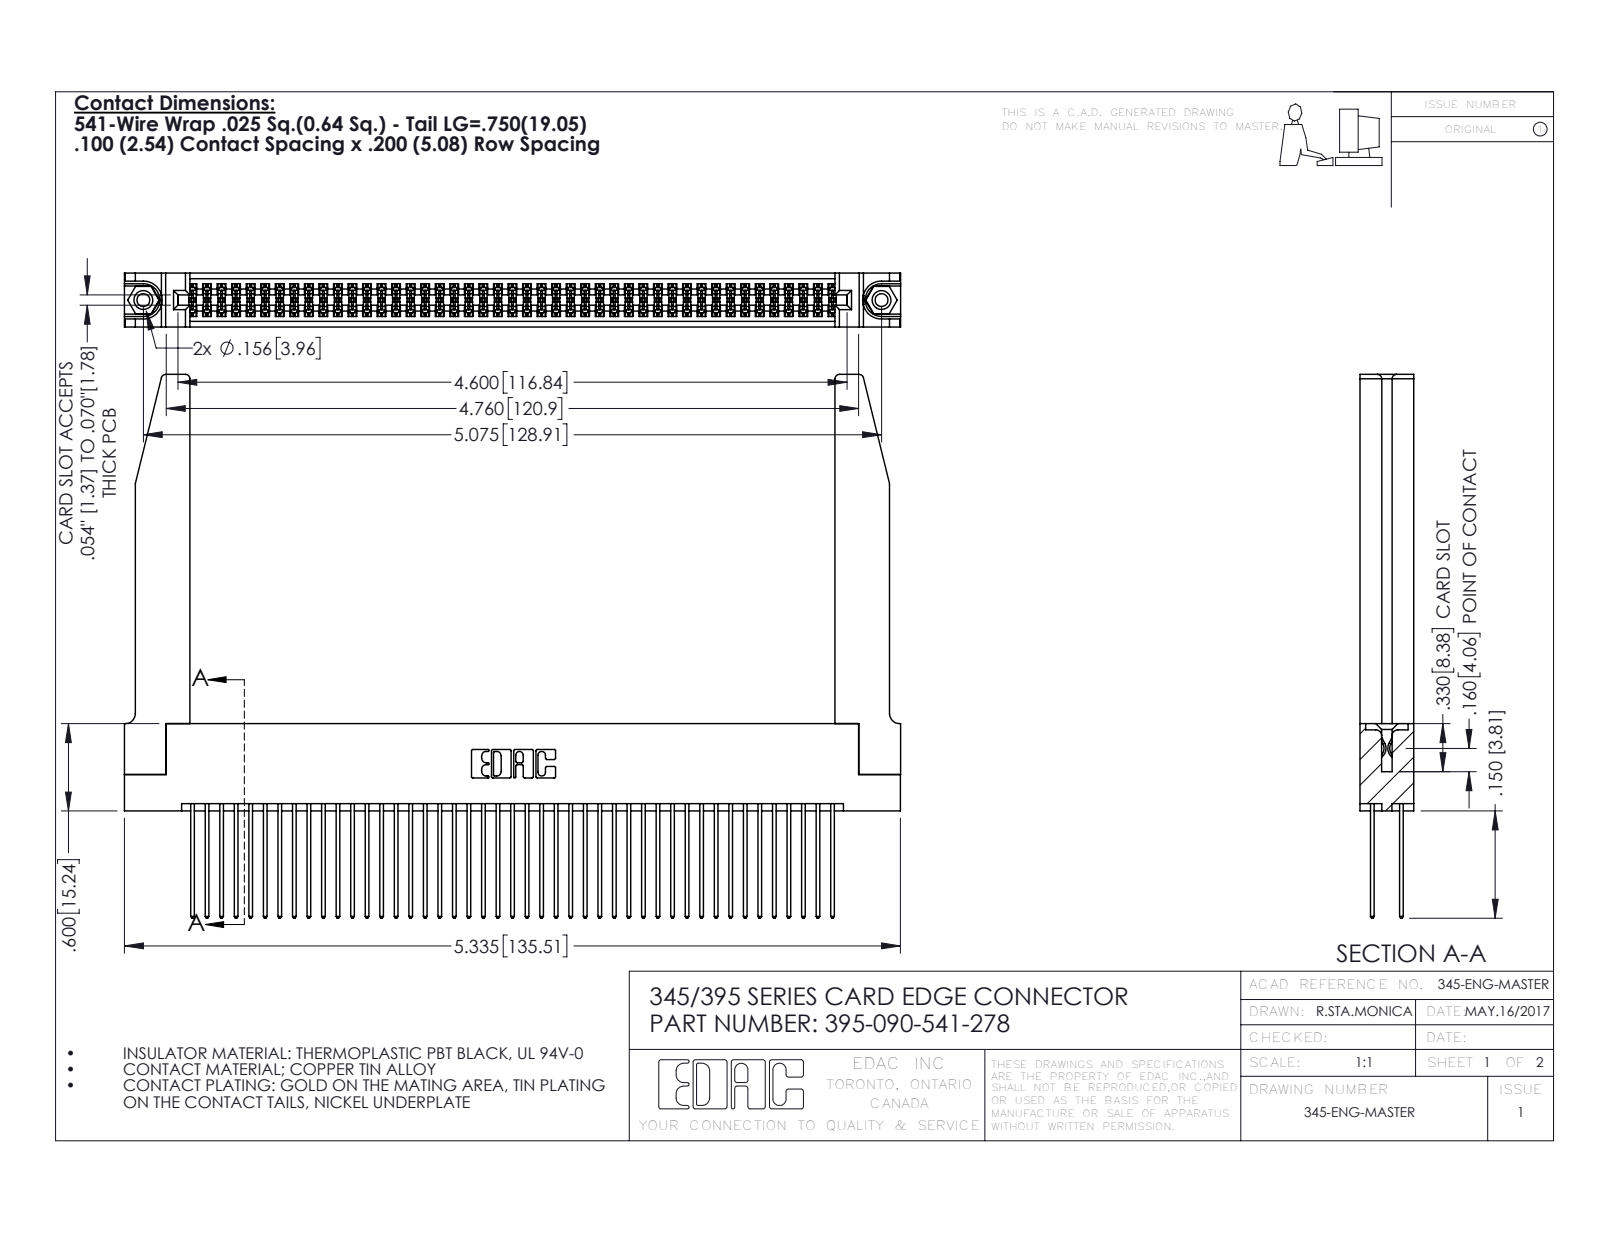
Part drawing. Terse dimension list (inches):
name: 345-292-001_345-293-141; 395-090-541-278; 345 Part_Flush Mounting Lugs - 0.156 Dia-TH; 345-220-078_345-220-078 (+1 more)
written by: SolidWorks 2016 (CONFIG_CONTROL_DESIGN)
unit: in
bodies: 95 solids, 4860 faces (3192 planar, 1616 cylindrical, 52 other)
size: 5.336 × 3.737 × 0.37
volume: 1.311 in³; area: 45.86 in²
holes: 2× ⌀0.089, 2× ⌀0.125, 2× ⌀0.156, 1× ⌀0.064
bosses: 2× ⌀0.155
rounds: 135× R0.006, 90× R0.01, 22× R0.01, 8× R0.03, 6× R0.007, 6× R0.031, 3× R0.026, 2× R0.014
face distances: 0.072, 0.298, 0.37, 0.2, 0.098, 0.272, 0.025, 0.225, 0.175, 0.148
hole spacings: 0.27, 4.839, 5.075
